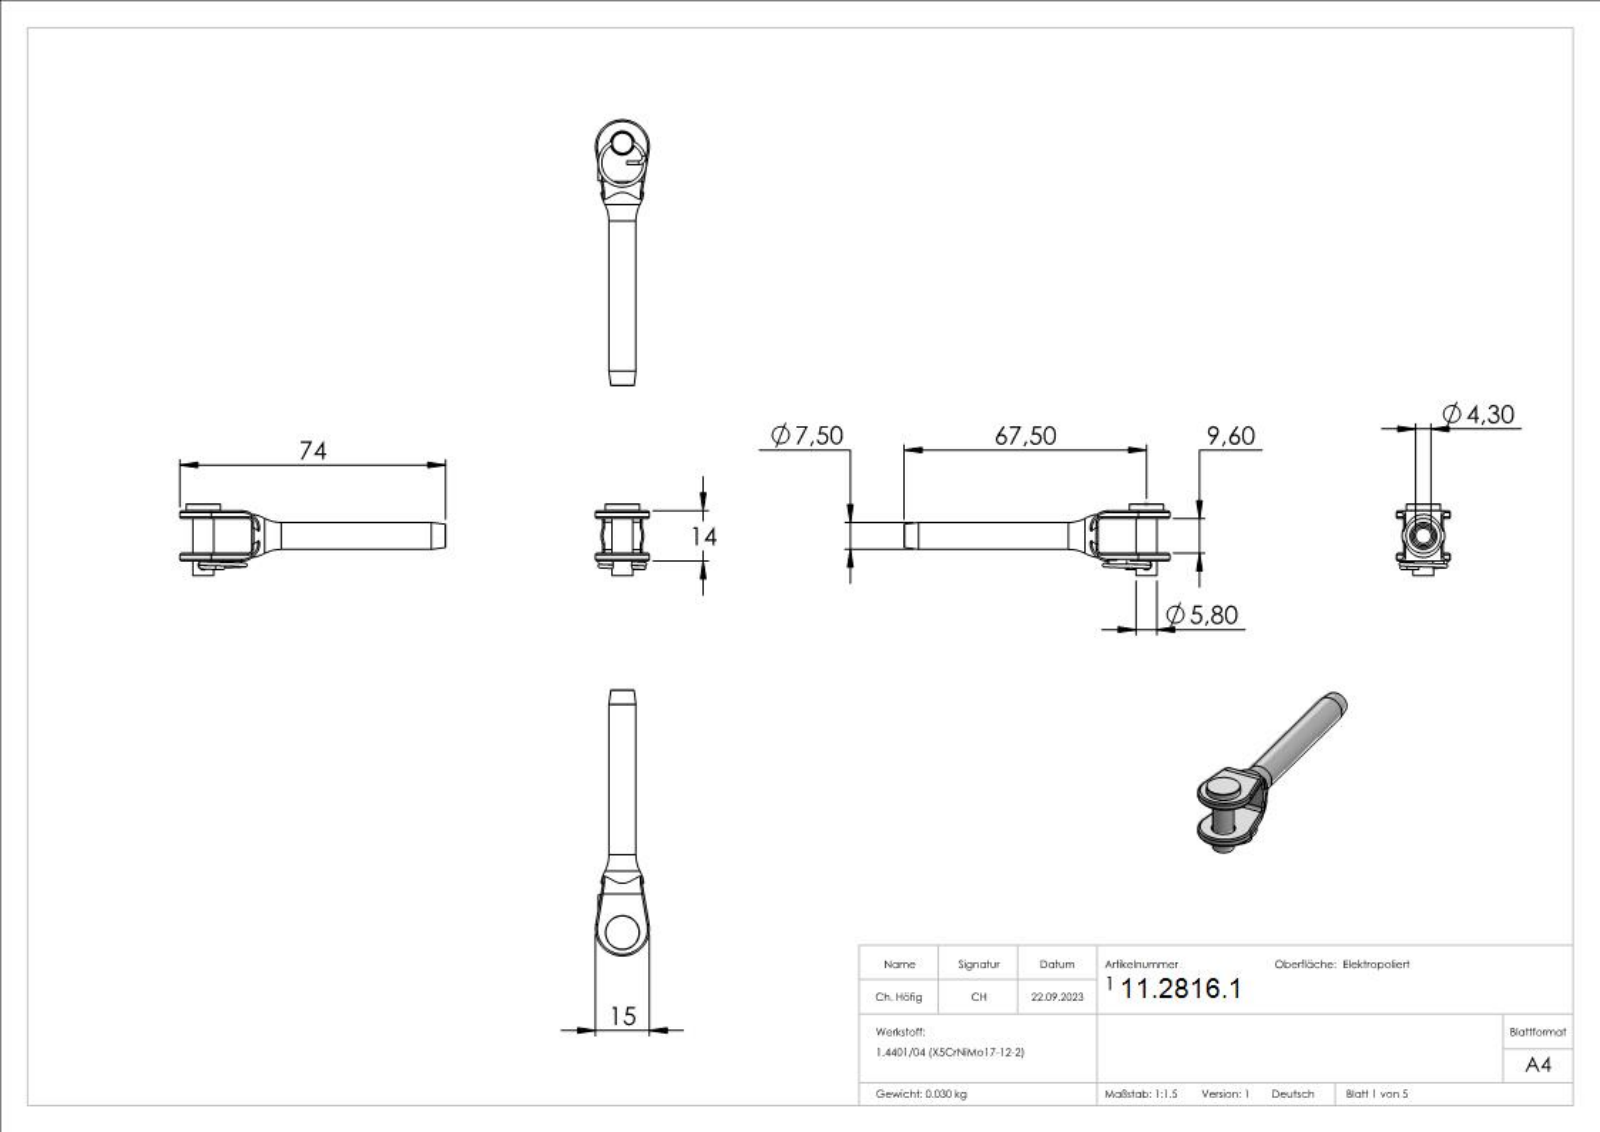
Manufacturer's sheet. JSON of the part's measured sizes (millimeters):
{"part_name": "101200X0X Teil3_101200303 Teil3; 101200X0X Teil2_101200404 Teil2; 101200X0X Teil1_101200404 Teil1; 101200404", "step_written_by": "SolidWorks 2018 (CONFIG_CONTROL_DESIGN)", "units": "millimeters", "bodies": {"solids": 3, "faces": 311, "planar": 118, "cylindrical": 63, "other": 130}, "overall_size": [74, 20, 15], "volume_mm3": 3695, "surface_area_mm2": 3864, "round_holes": [[2.5, 1], [4.3, 1], [6.5, 1]], "round_bosses_or_shafts": [[1, 2], [9.5, 1], [7.5, 1], [5.8, 1]], "partial_cylinders_radius": [[0.5, 12], [1, 2], [5, 2], [2.25, 1], [7.5, 1]], "face_to_face_distances": [2.2, 11.8, 9.6, 14, 4.1, 15.9, 13.7, 1.9, 6.3, 18.1]}
